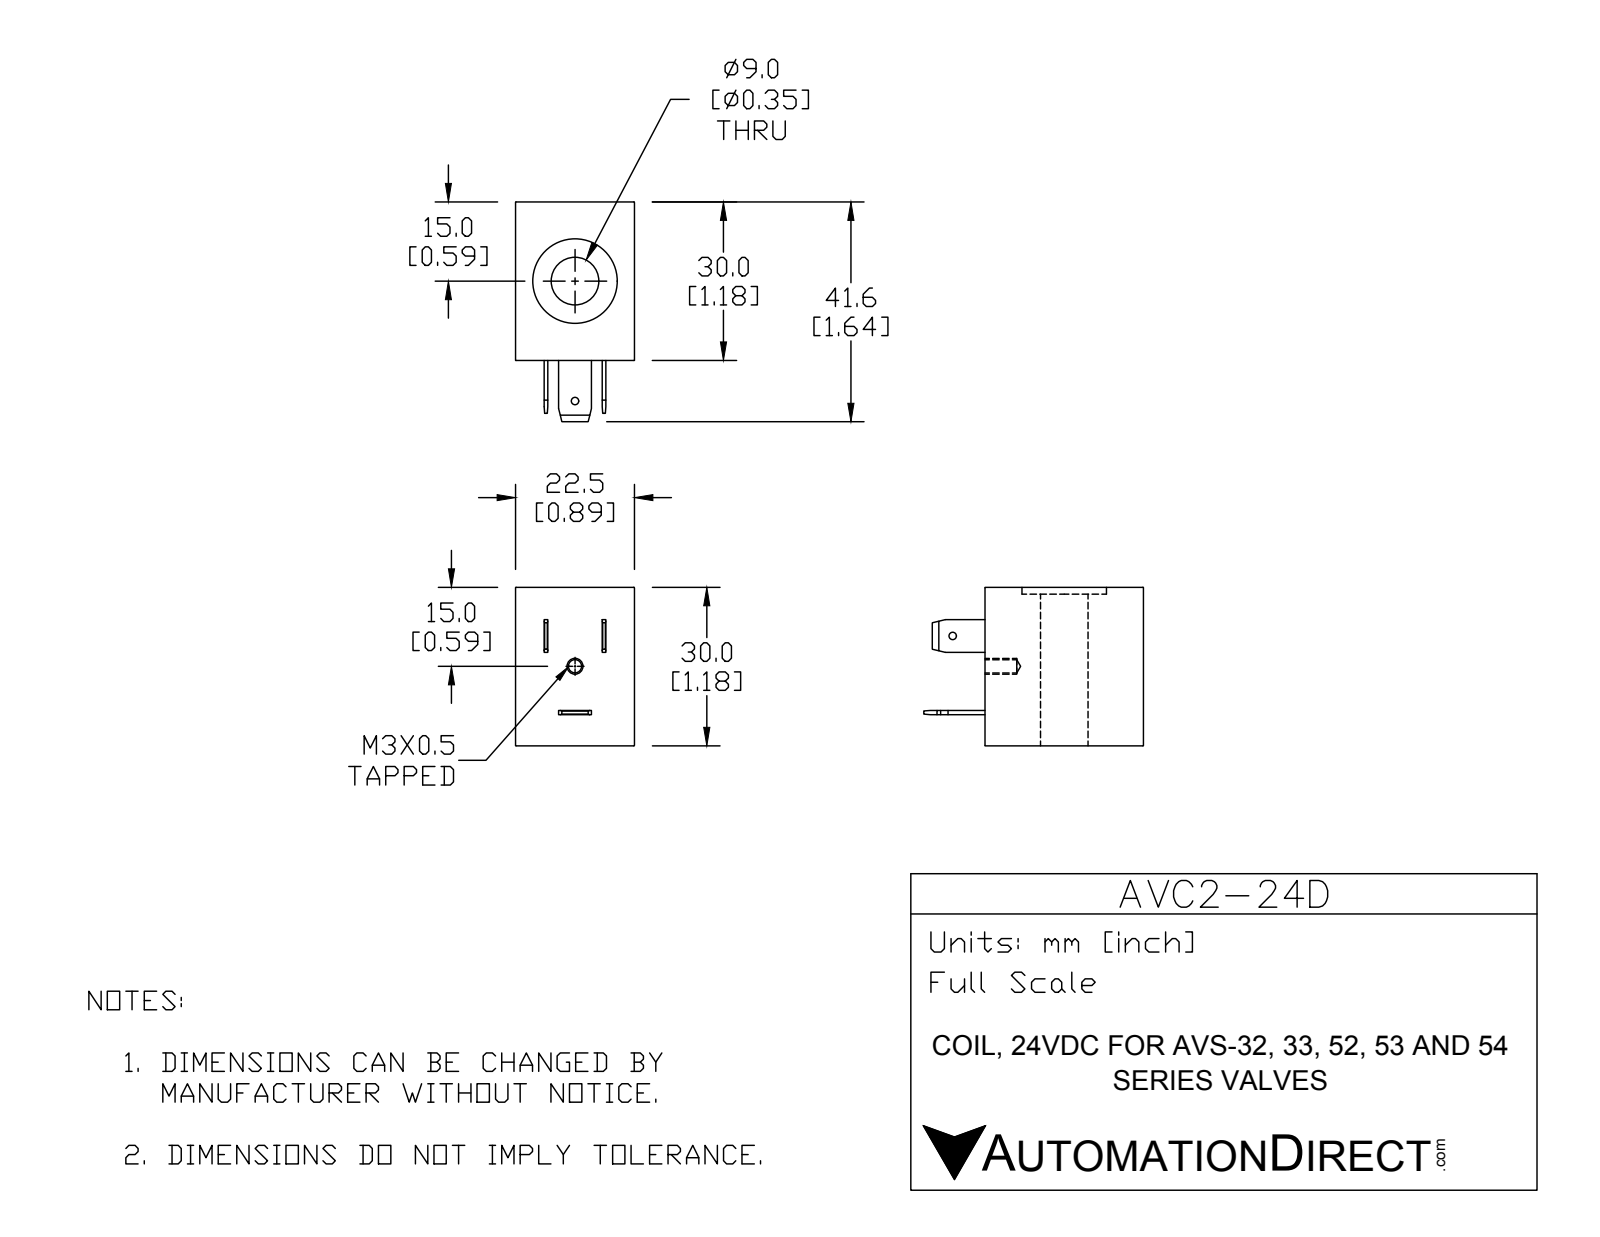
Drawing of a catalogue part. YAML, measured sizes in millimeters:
part_name: "AVC2-24D"
step_written_by: "SolidWorks 2016 (AUTOMOTIVE_DESIGN)"
units: millimeters
bodies: {solids: 1, faces: 60, planar: 34, cylindrical: 20, other: 6}
overall_size: [41.6, 30, 22.5]
volume: 18267
surface_area: 5712
round_holes:
  - {diameter: 1.4, count: 2}
  - {diameter: 2.5, count: 1}
  - {diameter: 9, count: 1}
  - {diameter: 16, count: 1}
partial_cylinders:
  - {radius: 0.1, count: 8}
face_to_face_distances: [30, 22.5, 28.7, 1.3, 11, 6.1, 16.4, 5.4, 17.1, 0.7]
hole_center_spacings: [22.7]
